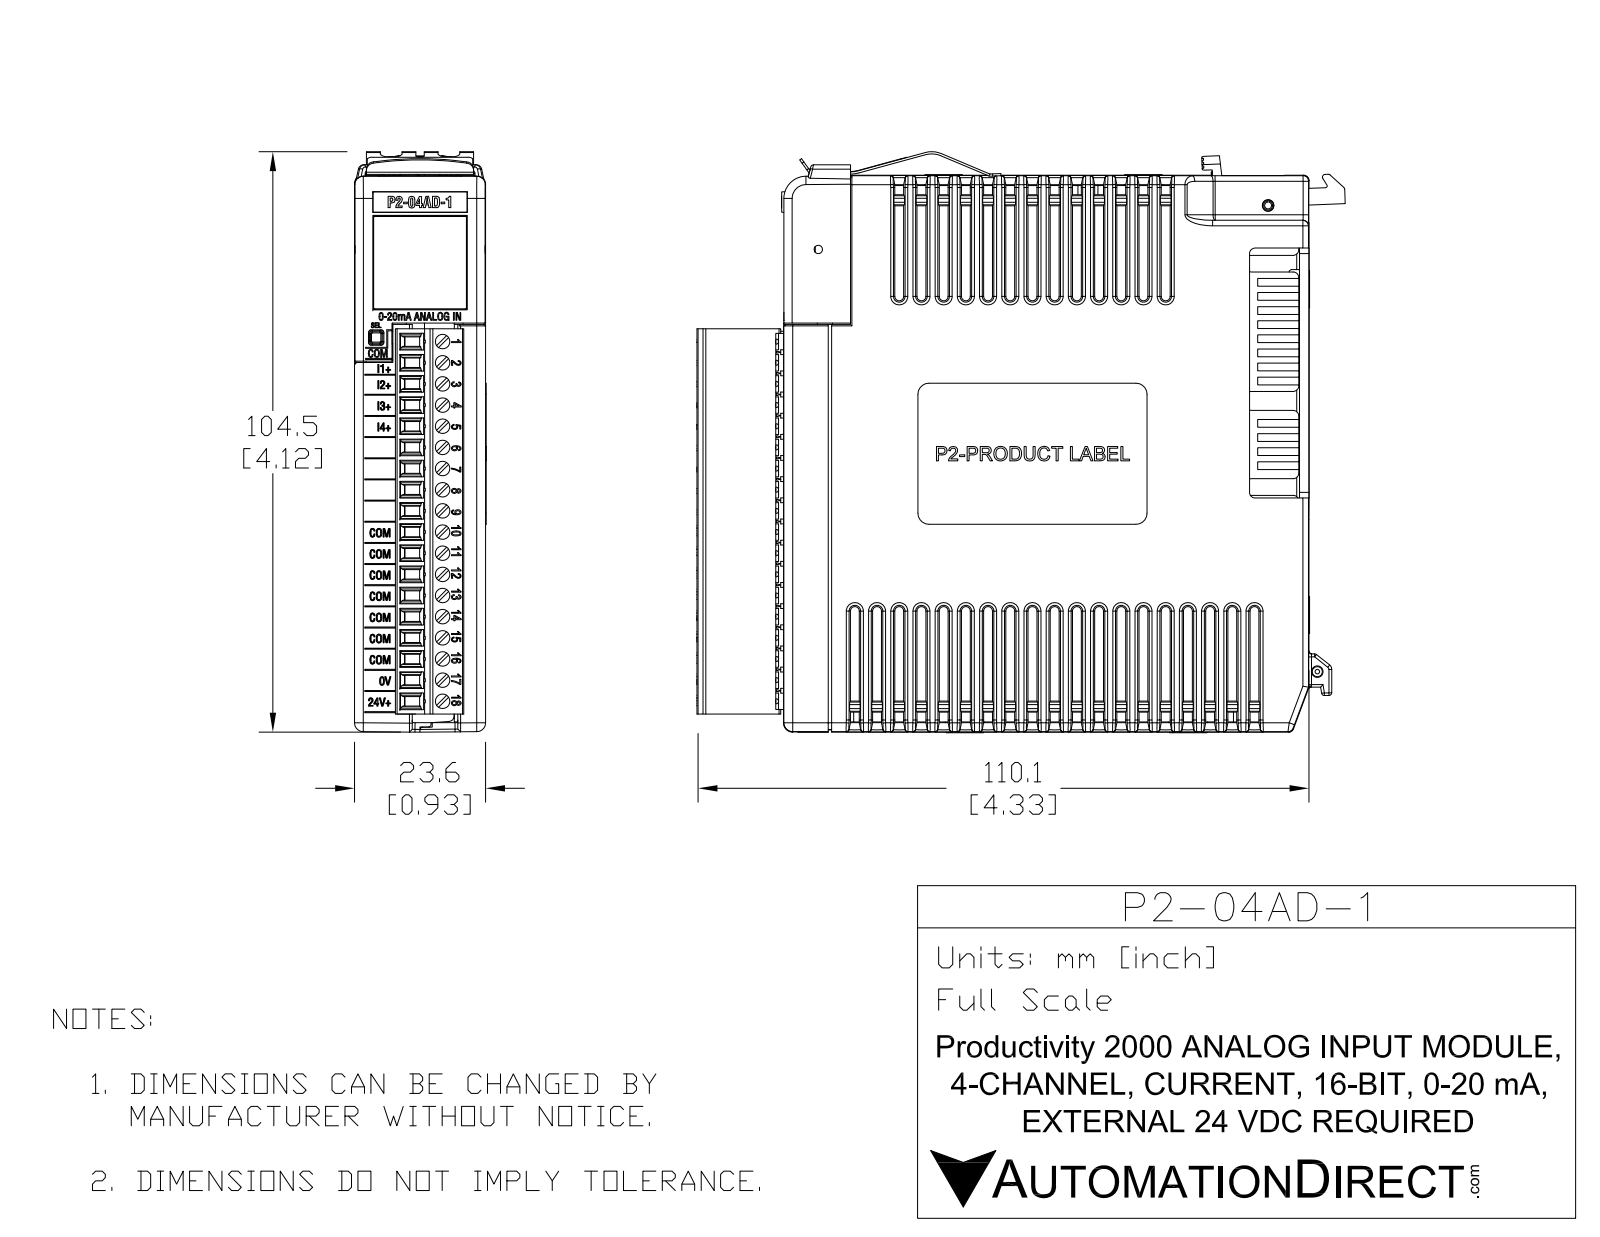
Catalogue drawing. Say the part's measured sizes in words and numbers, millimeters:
The part is named "P2-04AD-1 ext 1 comb 2 fXT B ext comb fXTc". Its 3-D file was written by "SolidWorks 2017 (AUTOMOTIVE_DESIGN)". It is 4 solids with 3452 faces: 2199 planar, 561 cylindrical and 692 other. Overall it measures 104.6 by 104.4 by 24.4 millimeters. Its volume is 209 300 cubic millimeters and its surface area 41 100 square millimeters. Round holes: 2 of diameter 1.2, 1 of diameter 1.5. Round bosses or shafts: 4 of diameter 0.4, 1 of diameter 0.7. Partial cylindrical surfaces (rounded edges, fillets, slot ends): 152 of radius 0.5, 112 of radius 0.2, 74 of radius 1, 20 of radius 1.5, 18 of radius 1.6, 13 of radius 1.6, 9 of radius 0.3, 6 of radius 2. The main face-to-face distances are 23.6, 6.4, 1.6, 18, 89.8, 0.4, 3.8, 6.4, 4.8, 94.6. The hole center spacings are 15.7.
